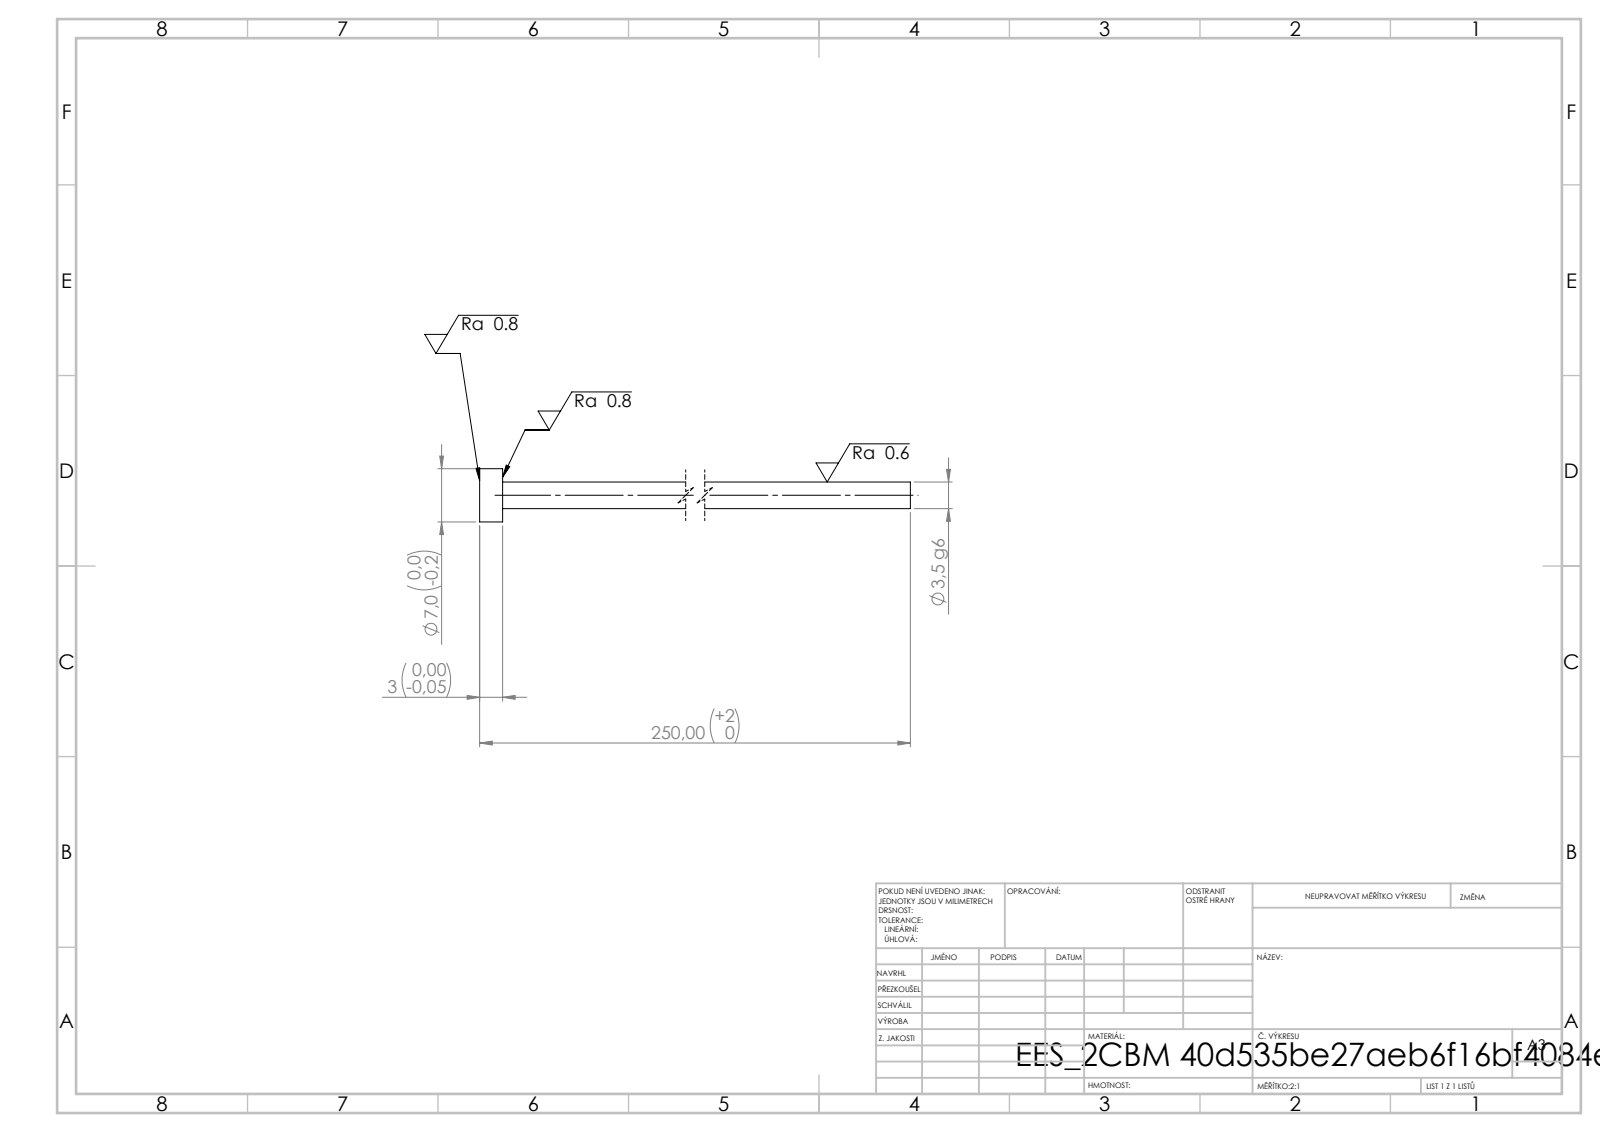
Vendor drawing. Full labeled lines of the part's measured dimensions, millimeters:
STEP written by: SolidWorks 2019 (CONFIG_CONTROL_DESIGN)
Units: millimetres
Bodies: 1 solid, 7 faces (3 planar, 4 cylindrical, 0 other)
Overall size (bounding box): 250 × 7 × 7
Volume: 2 492 mm³ · Surface area: 2 859 mm²
Round bosses / shafts (diameter × count): ⌀7 ×1, ⌀3.5 ×1
Main face-to-face distances: 3, 250, 247
